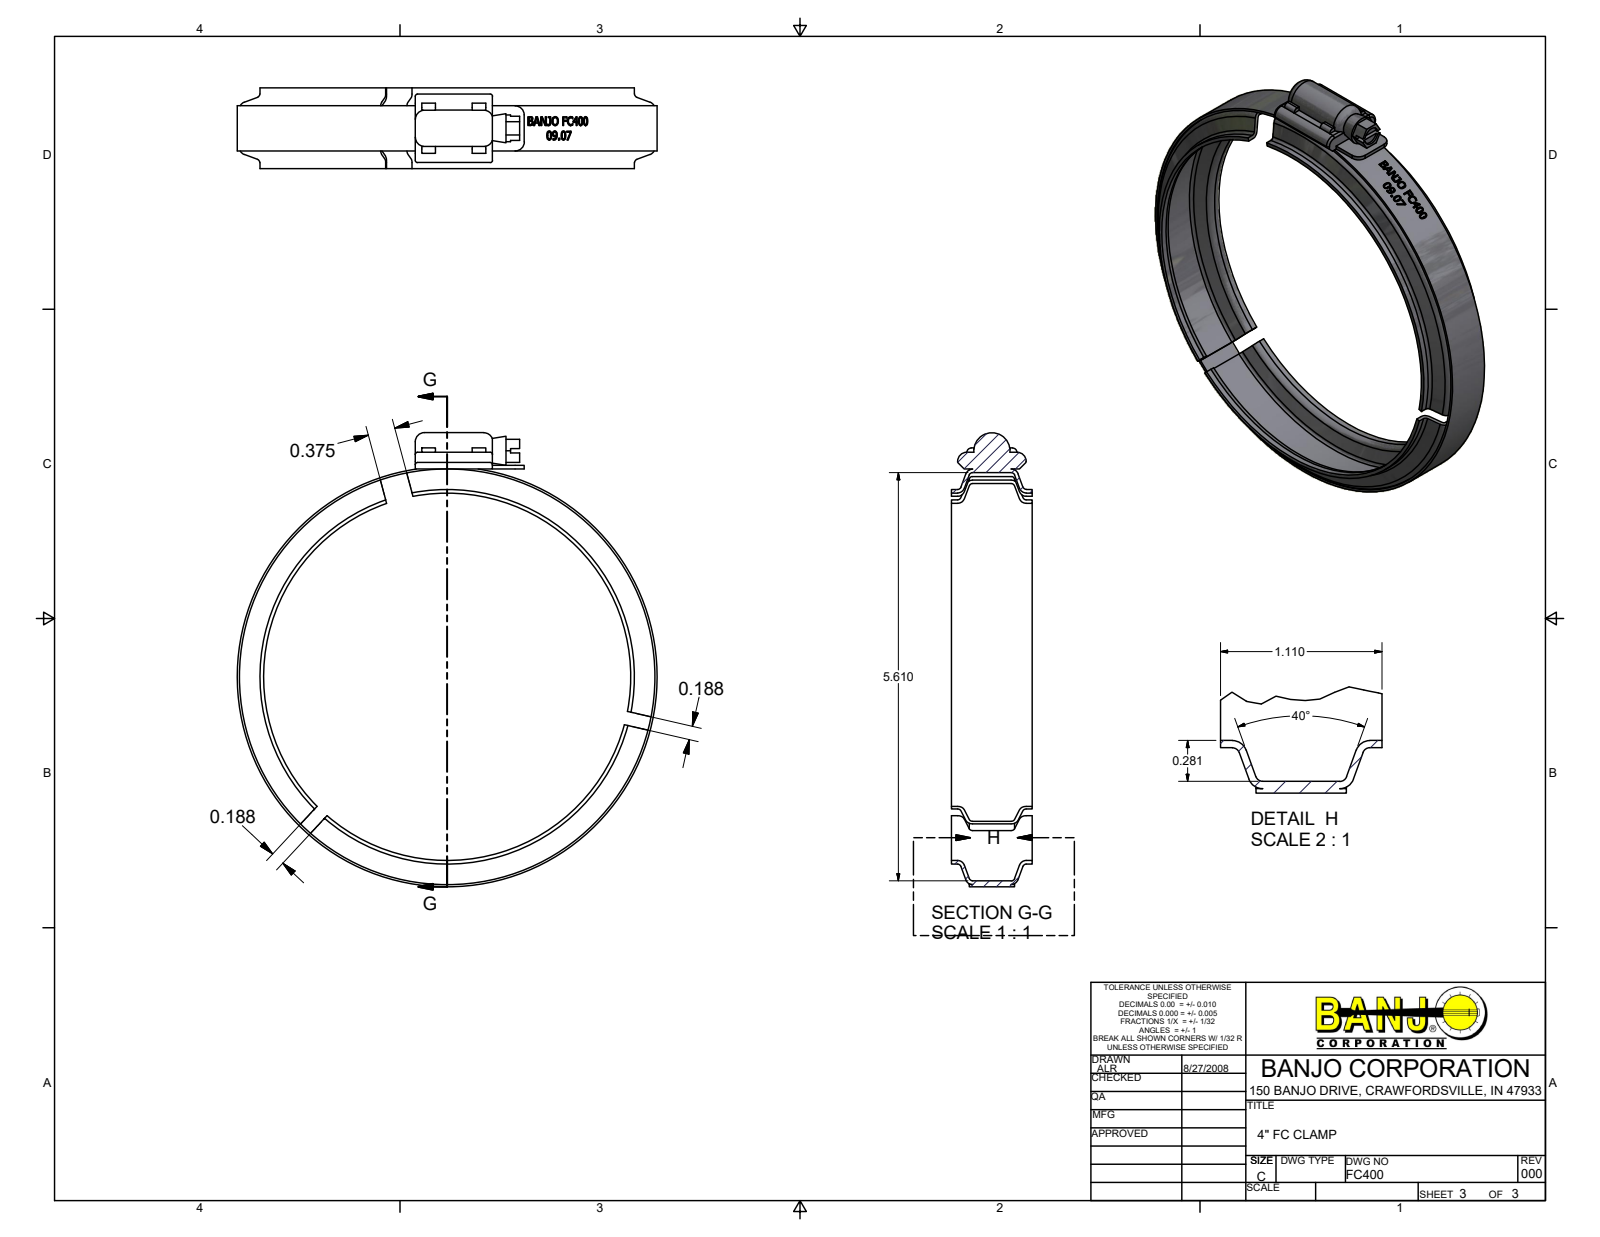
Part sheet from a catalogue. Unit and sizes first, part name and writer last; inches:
Units: inches
Overall size (bounding box): 6.241 × 5.773 × 1.11
Round holes (diameter × count): ⌀0.25 ×1, ⌀5.048 ×1, ⌀5.61 ×1, ⌀5.71 ×1
Round bosses / shafts (diameter × count): ⌀5.773 ×1, ⌀5.148 ×1
Partial cylindrical surfaces — rounded edges, fillets, slot ends (radius × count): R0.03 ×6, R0.125 ×4, R0.06 ×2, R0.25 ×1, R2.876 ×1
Main face-to-face distances: 0.244, 0.866, 1.11, 0.622, 0.05, 0.187, 0.23, 0.18, 1.06, 0.317
Volume: 1.902 in³ · Surface area: 58.06 in²
Bodies: 1 solid, 360 faces (128 planar, 61 cylindrical, 171 other)
Part name (STEP PRODUCT): FC400
STEP written by: Autodesk Inventor 2022 (CONFIG_CONTROL_DESIGN)
